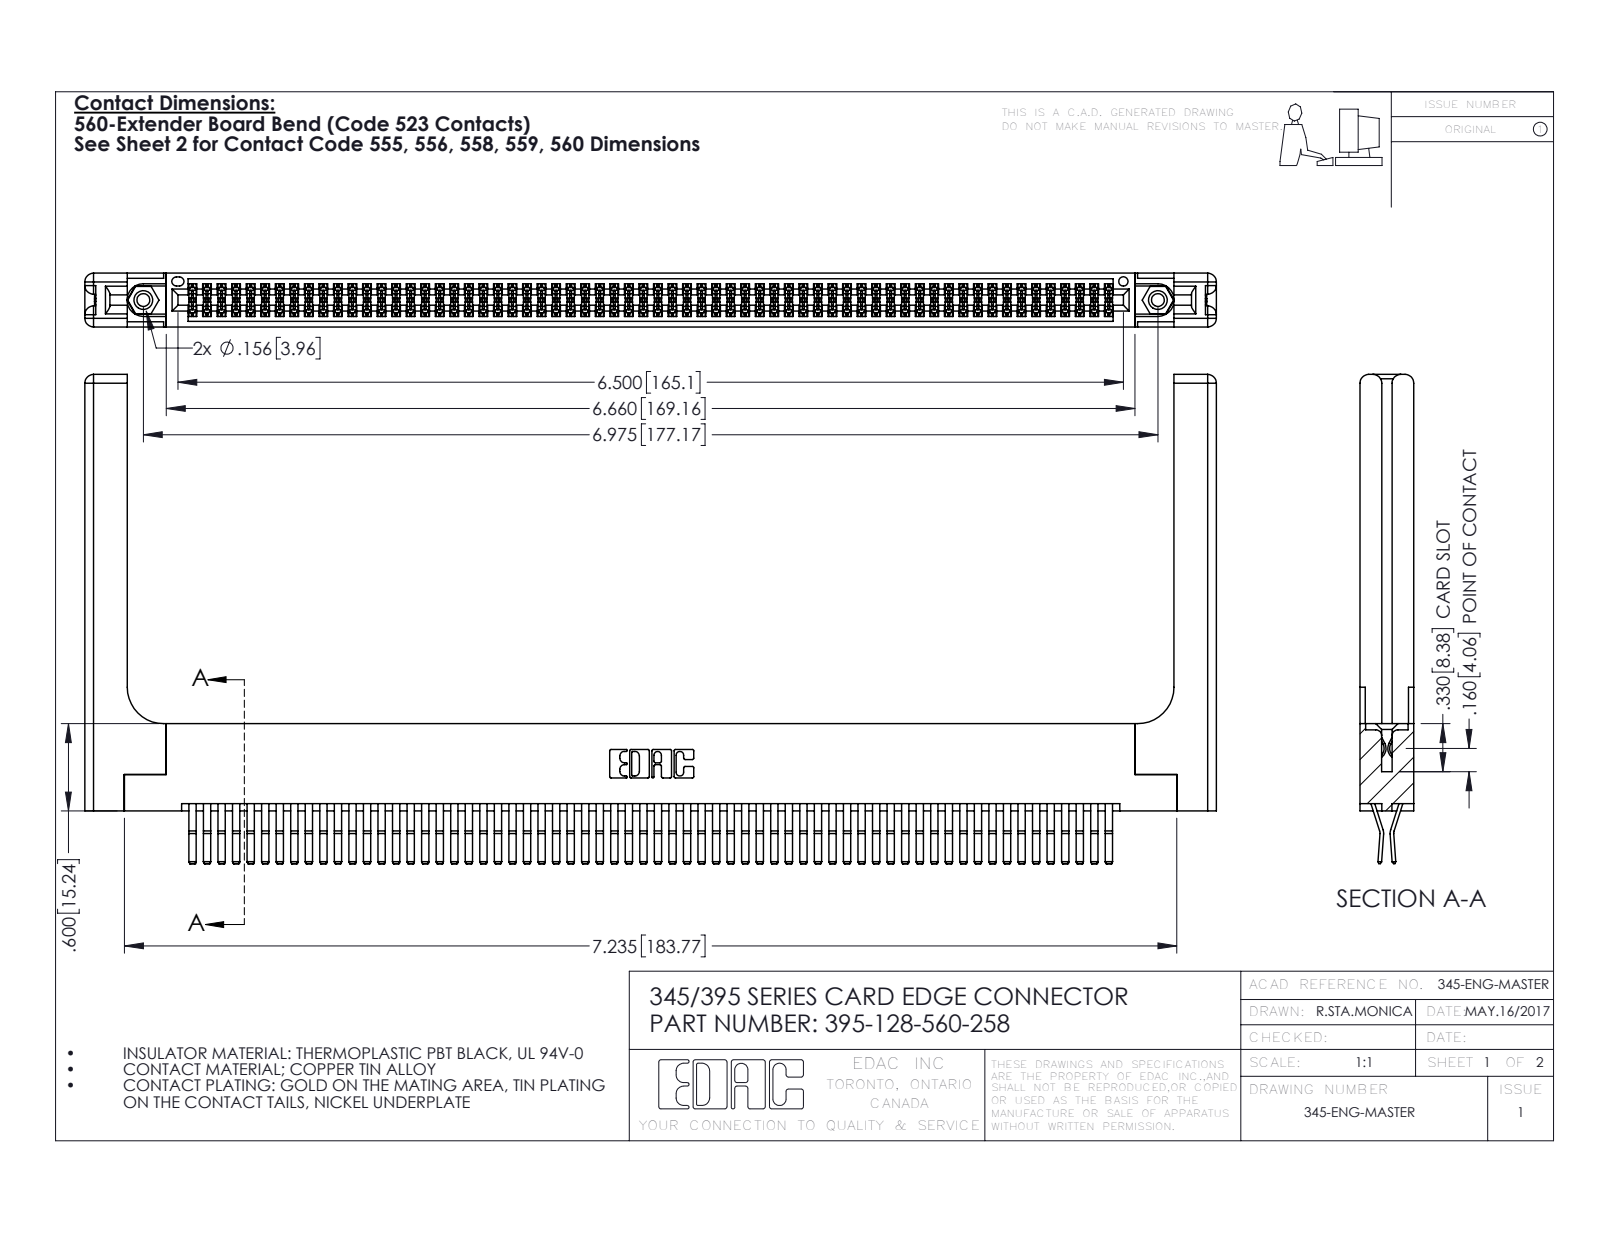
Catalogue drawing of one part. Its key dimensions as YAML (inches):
part_name: "395-128-560-258; 345-250-001_345-250-001-102; 345 Part_Flush Mounting Lugs - 0.156 Dia-TH; 345-292-001_560 Tail (+1 more)"
step_written_by: "SolidWorks 2016 (CONFIG_CONTROL_DESIGN)"
units: inches
bodies: {solids: 133, faces: 7038, planar: 4452, cylindrical: 2526, other: 60}
overall_size: [7.779, 3.362, 0.37]
volume: 1.752
surface_area: 58.21
round_holes:
  - {diameter: 0.089, count: 2}
  - {diameter: 0.125, count: 2}
  - {diameter: 0.156, count: 2}
  - {diameter: 0.064, count: 1}
round_bosses_or_shafts:
  - {diameter: 0.155, count: 2}
partial_cylinders:
  - {radius: 0.006, count: 192}
  - {radius: 0.01, count: 22}
  - {radius: 0.06, count: 16}
  - {radius: 0.007, count: 6}
  - {radius: 0.031, count: 6}
  - {radius: 0.026, count: 3}
  - {radius: 0.01, count: 2}
  - {radius: 0.014, count: 2}
face_to_face_distances: [0.072, 0.298, 0.025, 0.37, 0.2, 0.098, 0.272, 0.225, 0.148, 0.15]
hole_center_spacings: [0.27, 6.739, 6.975]
